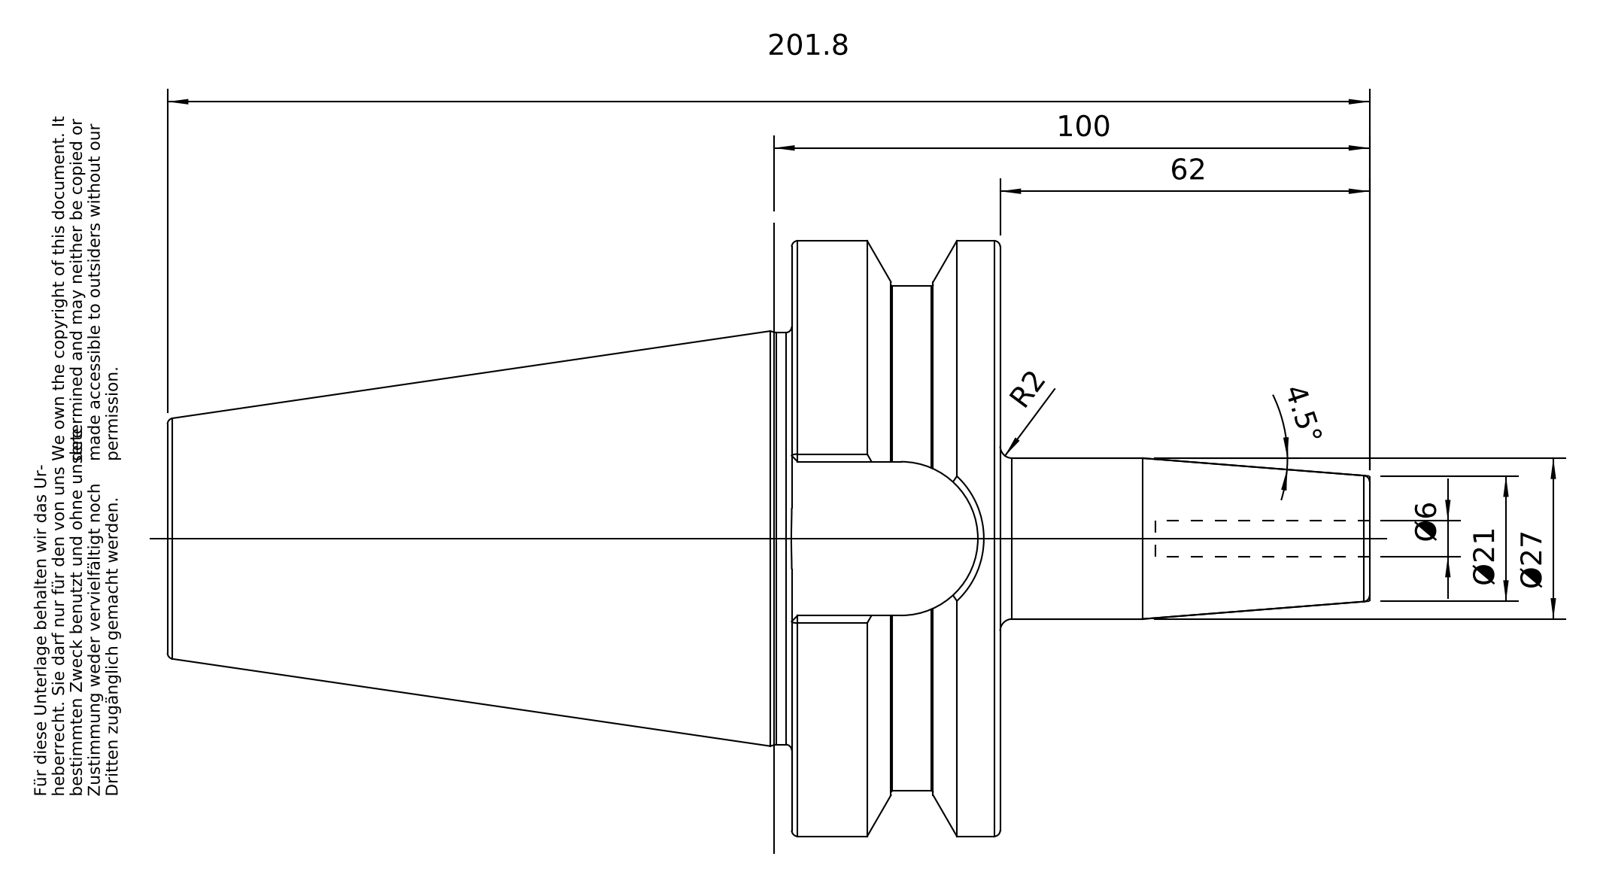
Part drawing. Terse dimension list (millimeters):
name: 50-640-06
written by: PRO/ENGINEER BY PARAMETRIC TECHNOLOGY CORPORATION, 2010430 (CONFIG_CONTROL_DESIGN)
unit: mm
bodies: 1 solid, 96 faces (26 planar, 22 cylindrical, 48 other)
size: 201.8 × 99.97 × 99.97
volume: 498 100 mm³; area: 57 114 mm²
holes: 1× ⌀6, 1× ⌀20.75, 1× ⌀25.02, 1× ⌀25.7
bosses: 1× ⌀99.97, 1× ⌀84.75, 1× ⌀69.15, 1× ⌀27, 1× ⌀24.01
rounds: 1× R12.9
face distances: 35, 70.4, 104.8, 139.8, 25.8, 201.8, 97, 62, 48, 56.8
